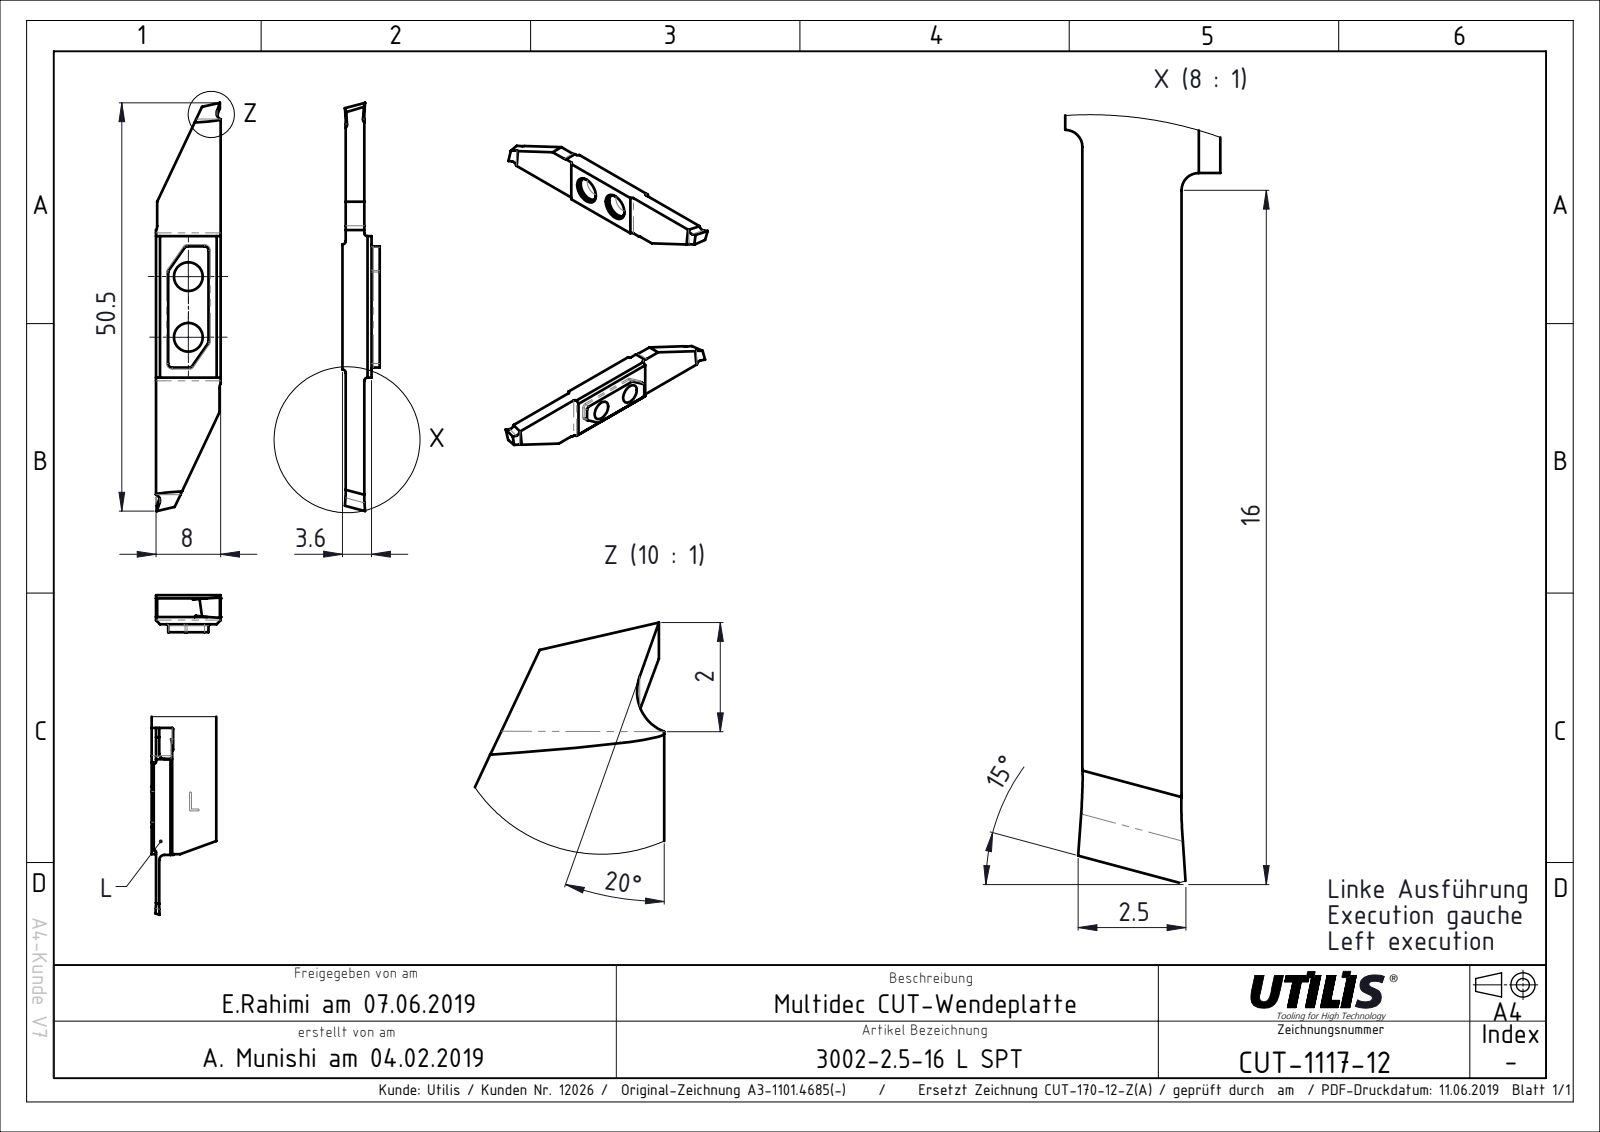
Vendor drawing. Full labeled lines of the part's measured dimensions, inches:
Part name (STEP PRODUCT): CUT-1117; ASME Y14.5
STEP written by: FormatWorks Professional (AP242_MANAGED_MODEL_BASED_3D_ENGINEERING_MIM_LF)
Units: inches
Bodies: 1 solid, 34 faces (24 planar, 10 cylindrical, 0 other)
Overall size (bounding box): 1.988 × 0.315 × 0.142
Volume: 0.052 in³ · Surface area: 1.54 in²
Round holes (diameter × count): ⌀0.14 ×2
Partial cylindrical surfaces — rounded edges, fillets, slot ends (radius × count): R0.016 ×4, R0.039 ×2
Main face-to-face distances: 0.09, 0.016, 0.106, 0.142, 0.126, 0.036, 0.315, 0.712, 0.309, 0.303
Hole centre spacings: 0.295
